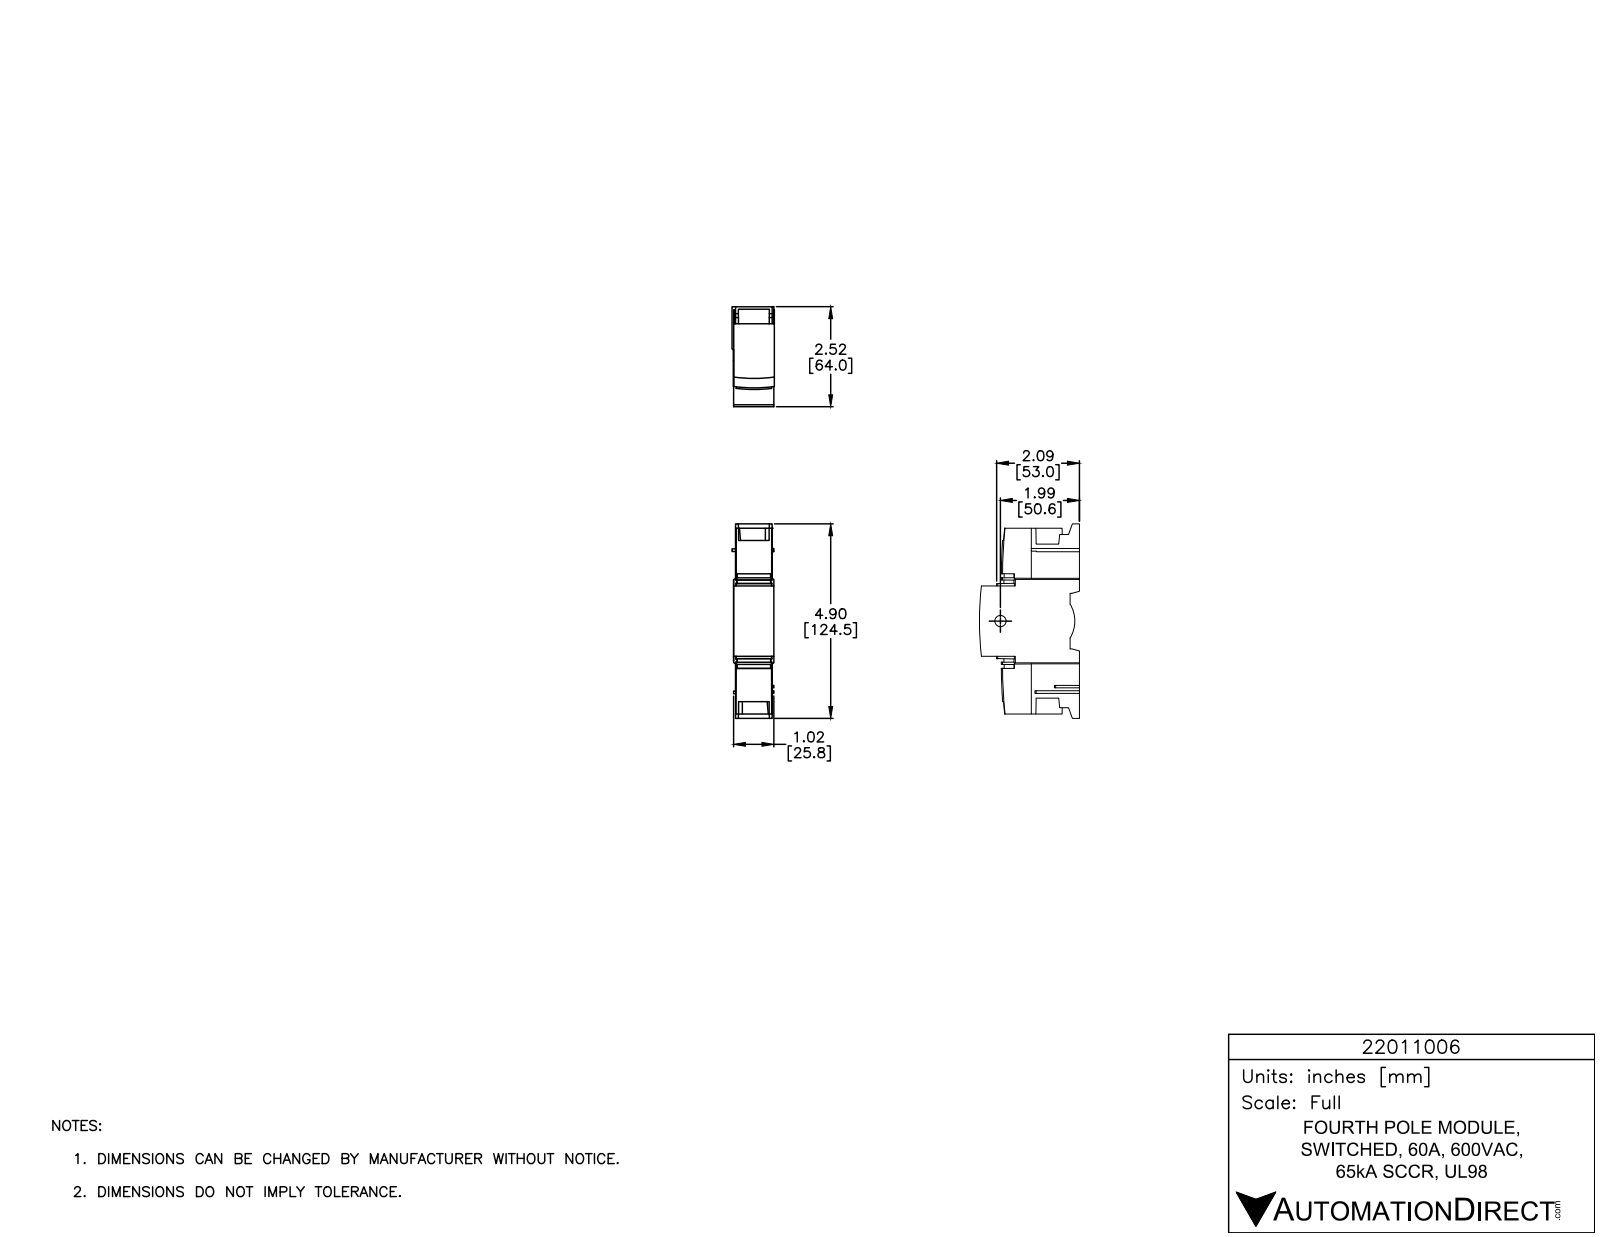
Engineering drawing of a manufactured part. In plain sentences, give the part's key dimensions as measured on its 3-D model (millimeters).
The part is named "22011006". Its 3-D file was written by "SolidWorks 2015 (AUTOMOTIVE_DESIGN)". It is 1 solid with 166 faces: 151 planar, 11 cylindrical and 4 other. Overall it measures 124.5 by 64 by 26.8 millimeters. Its volume is 130 100 cubic millimeters and its surface area 27 980 square millimeters. Round holes: 1 of diameter 7.2. Partial cylindrical surfaces (rounded edges, fillets, slot ends): 1 of radius 21, 1 of radius 90, 1 of radius 92.6, 1 of radius 200. The main face-to-face distances are 25.8, 1.3, 24.5, 24.7, 23.4, 1.1, 14, 4.3, 19.1, 30.2.
